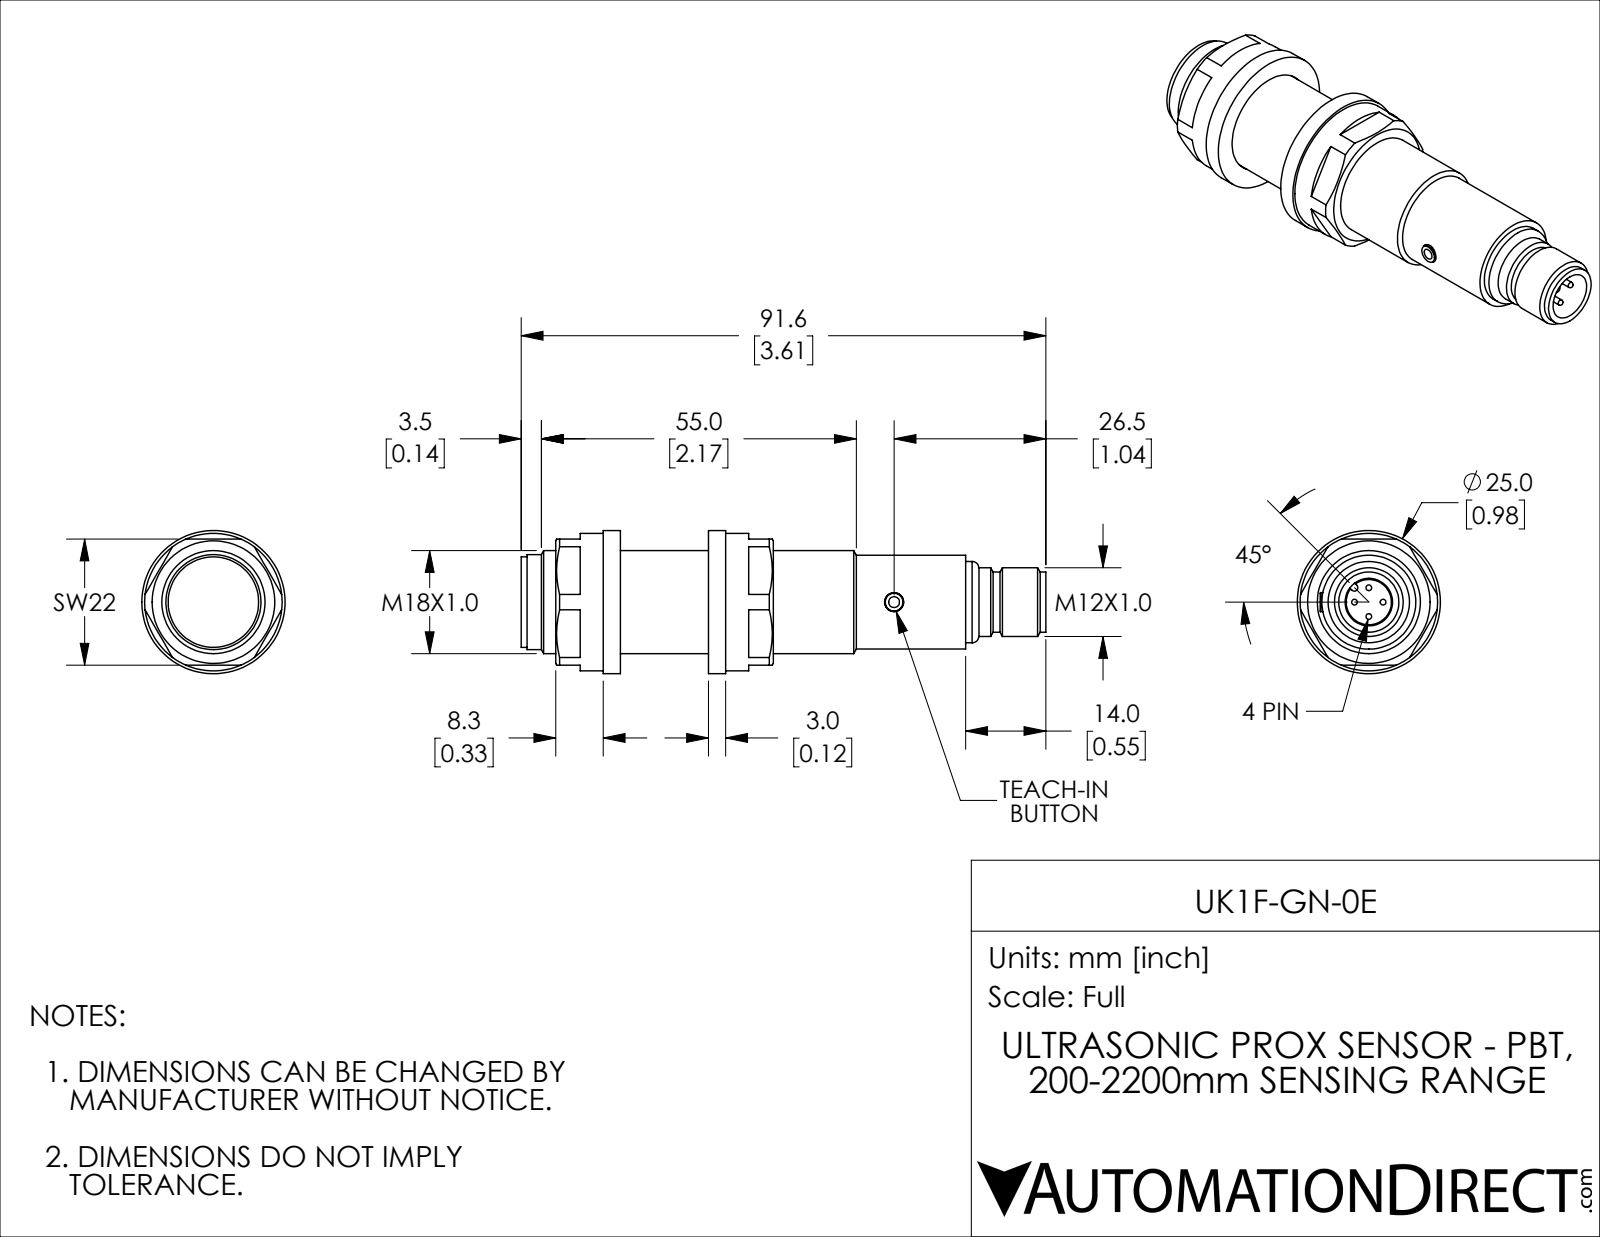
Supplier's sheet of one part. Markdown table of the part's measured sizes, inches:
| quantity | value |
| --- | --- |
| part name | UK1F-GN-0E |
| STEP written by | SolidWorks 2018 (AUTOMOTIVE_DESIGN) |
| units | inches |
| bodies | 6 solids, 123 faces (43 planar, 49 cylindrical, 31 other) |
| overall size | 3.606 × 0.984 × 0.984 |
| volume | 1.477 in³ |
| surface area | 16.01 in² |
| round holes (diameter × count) | 0.13 × 1, 0.327 × 1, 0.709 × 1, 0.717 × 1 |
| round bosses / shafts (diameter × count) | 0.039 × 4, 0.984 × 1, 0.945 × 1, 0.654 × 1, 0.646 × 1, 0.622 × 1, 0.559 × 1, 0.472 × 1 |
| partial cylindrical surfaces (radius × count) | 0.024 × 1 |
| main face-to-face distances | 0.118, 0.724, 0.843, 0.606, 0.866, 0.327, 0.445, 1.051, 1.169, 0.563 |
